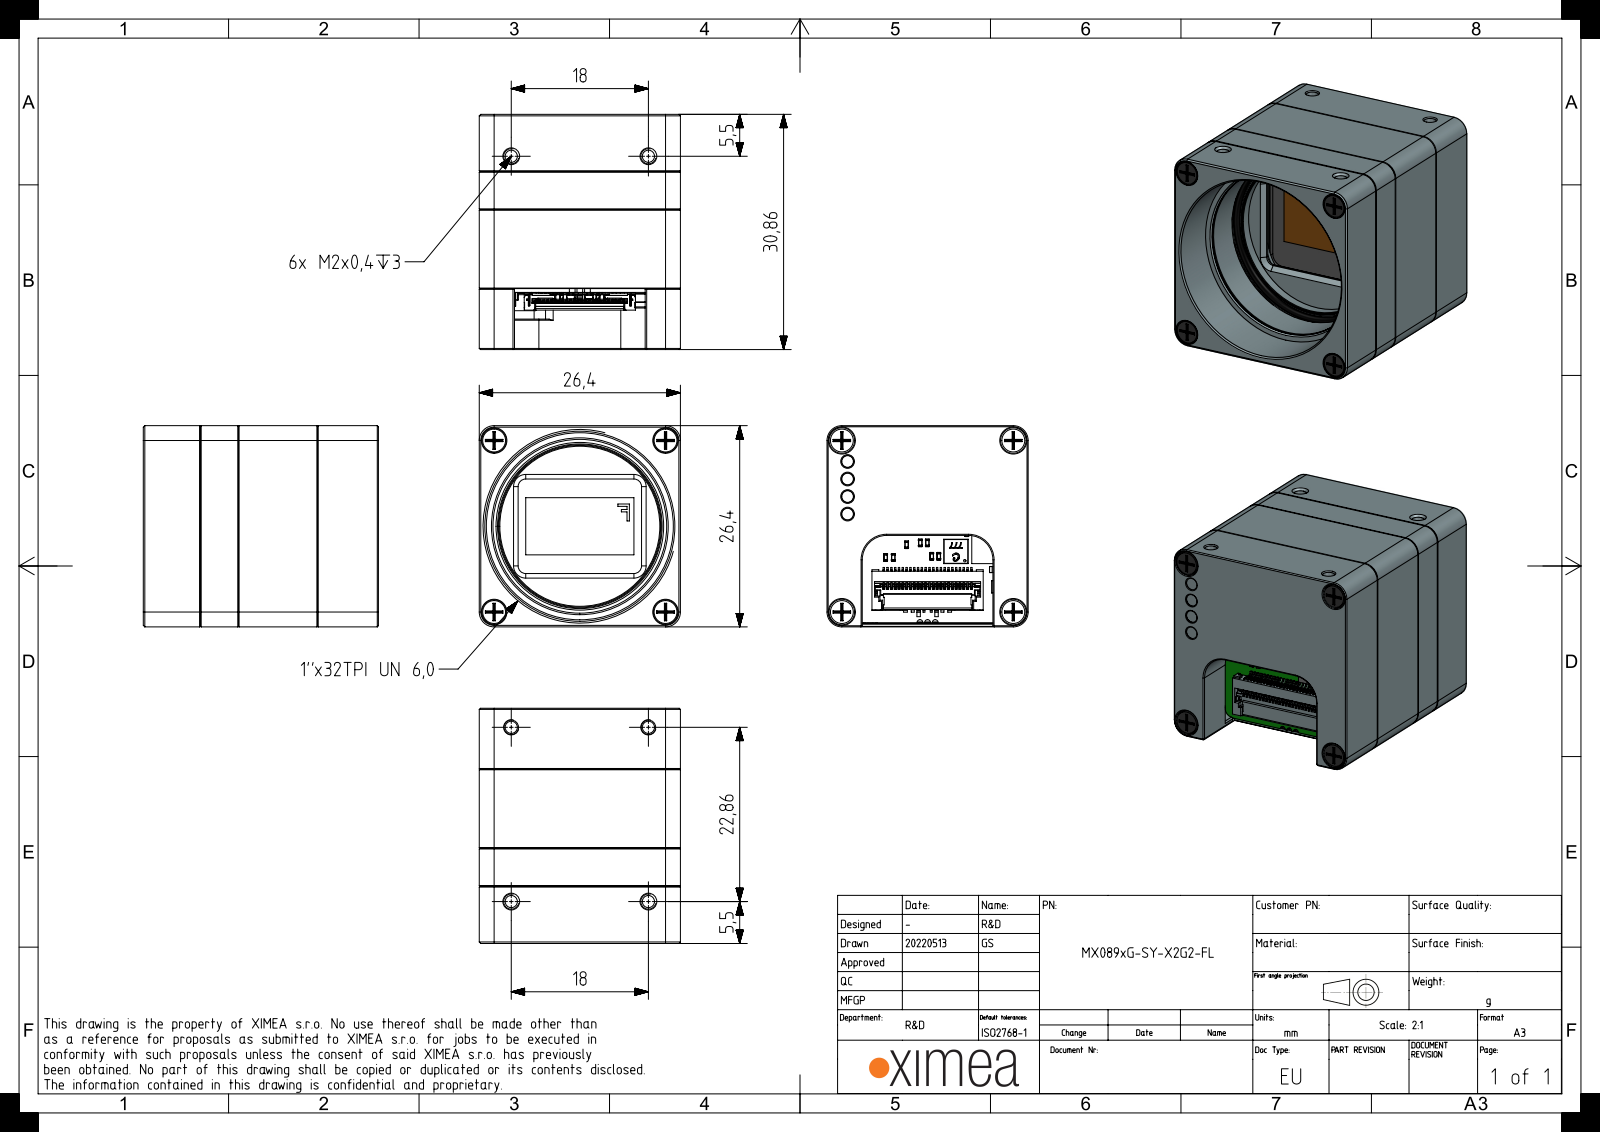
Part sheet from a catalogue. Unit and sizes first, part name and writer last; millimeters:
Units: millimetres
Overall size (bounding box): 30.9 × 26.4 × 26.4
Round holes (diameter × count): ⌀1.6 ×12, ⌀0.9 ×4, ⌀2 ×4, ⌀2.1 ×4, ⌀3 ×4, ⌀3.2 ×4, ⌀3.4 ×4, ⌀1.3 ×2, ⌀1.7 ×2, ⌀21 ×1, ⌀22.8 ×1, ⌀24.4 ×1
Round bosses / shafts (diameter × count): ⌀1.9 ×4, ⌀1.6 ×4, ⌀0.8 ×4, ⌀3 ×2, ⌀1.6 ×2, ⌀25 ×1, ⌀21.6 ×1
Partial cylindrical surfaces — rounded edges, fillets, slot ends (radius × count): R0.3 ×17, R1.5 ×15, R0.1 ×14, R0.2 ×14, R1 ×14, R0.4 ×12, R0.2 ×10, R0.3 ×8
Main face-to-face distances: 1, 26.4, 3.6, 11.5, 6.9, 2.5, 4.6, 10.5, 10.4, 6.8
Hole centre spacings: 15.9, 22.5, 2.3, 3.8, 4.6, 13.5, 18, 18.7
Volume: 10 300 mm³ · Surface area: 17 290 mm²
Bodies: 32 solids, 7565 faces (5197 planar, 2093 cylindrical, 275 other)
Part name (STEP PRODUCT): MECH-O-RING-22X1-VI370; MT089xG-PR-SENSOR-PCA; FLT-BK7-AR2X-D25; SROB-M1.6x3-SLOT-STNLS (+8 more)
STEP written by: SIEMENS PLM Software NX 1907 (AUTOMOTIVE_DESIGN)
